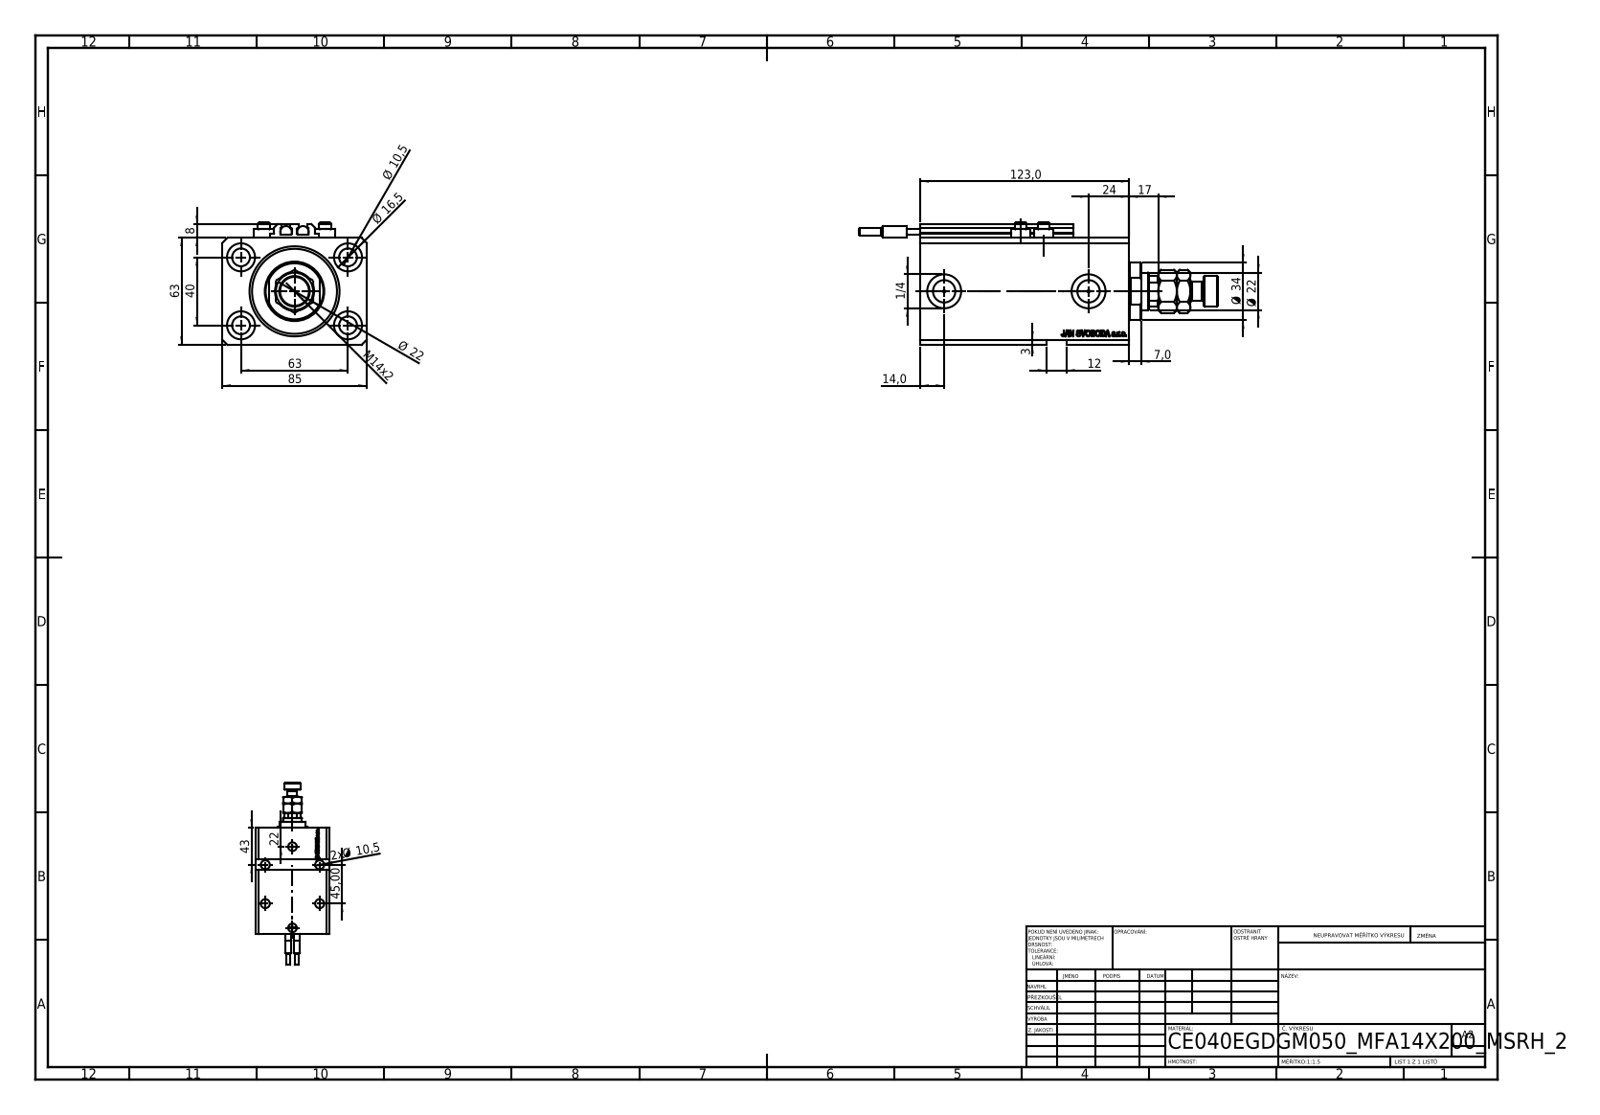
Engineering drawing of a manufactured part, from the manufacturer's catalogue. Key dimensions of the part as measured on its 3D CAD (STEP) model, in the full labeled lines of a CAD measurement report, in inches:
Part name (STEP PRODUCT): MFA; V250CE_E_Body; V250CE_C_VCP; ALLEN BOLT V250CE (+2 more)
STEP written by: SolidWorks 2019 (CONFIG_CONTROL_DESIGN)
Units: inches
Bodies: 11 solids, 1227 faces (587 planar, 174 cylindrical, 466 other)
Overall size (bounding box): 8.307 × 3.346 × 2.835
Volume: 34.62 in³ · Surface area: 196 in²
Round holes (diameter × count): ⌀0.413 ×8, ⌀0.049 ×4, ⌀0.157 ×4, ⌀0.65 ×4, ⌀0.394 ×2, ⌀0.518 ×2, ⌀0.787 ×2, ⌀0.492 ×1, ⌀0.866 ×1, ⌀1.575 ×1, ⌀2.087 ×1
Round bosses / shafts (diameter × count): ⌀0.457 ×4, ⌀0.276 ×4, ⌀0.268 ×2, ⌀0.256 ×2, ⌀0.157 ×2, ⌀1.339 ×1, ⌀0.709 ×1, ⌀0.433 ×1
Partial cylindrical surfaces — rounded edges, fillets, slot ends (radius × count): R0.008 ×10, R0.413 ×1
Main face-to-face distances: 2.48, 3.346, 0.669, 4.843, 4.173, 0.449, 3.724, 4.394, 0.118, 2.559
Hole centre spacings: 1.469, 2.48, 0.535, 0.606, 0.983, 1.084, 1.324, 1.417
